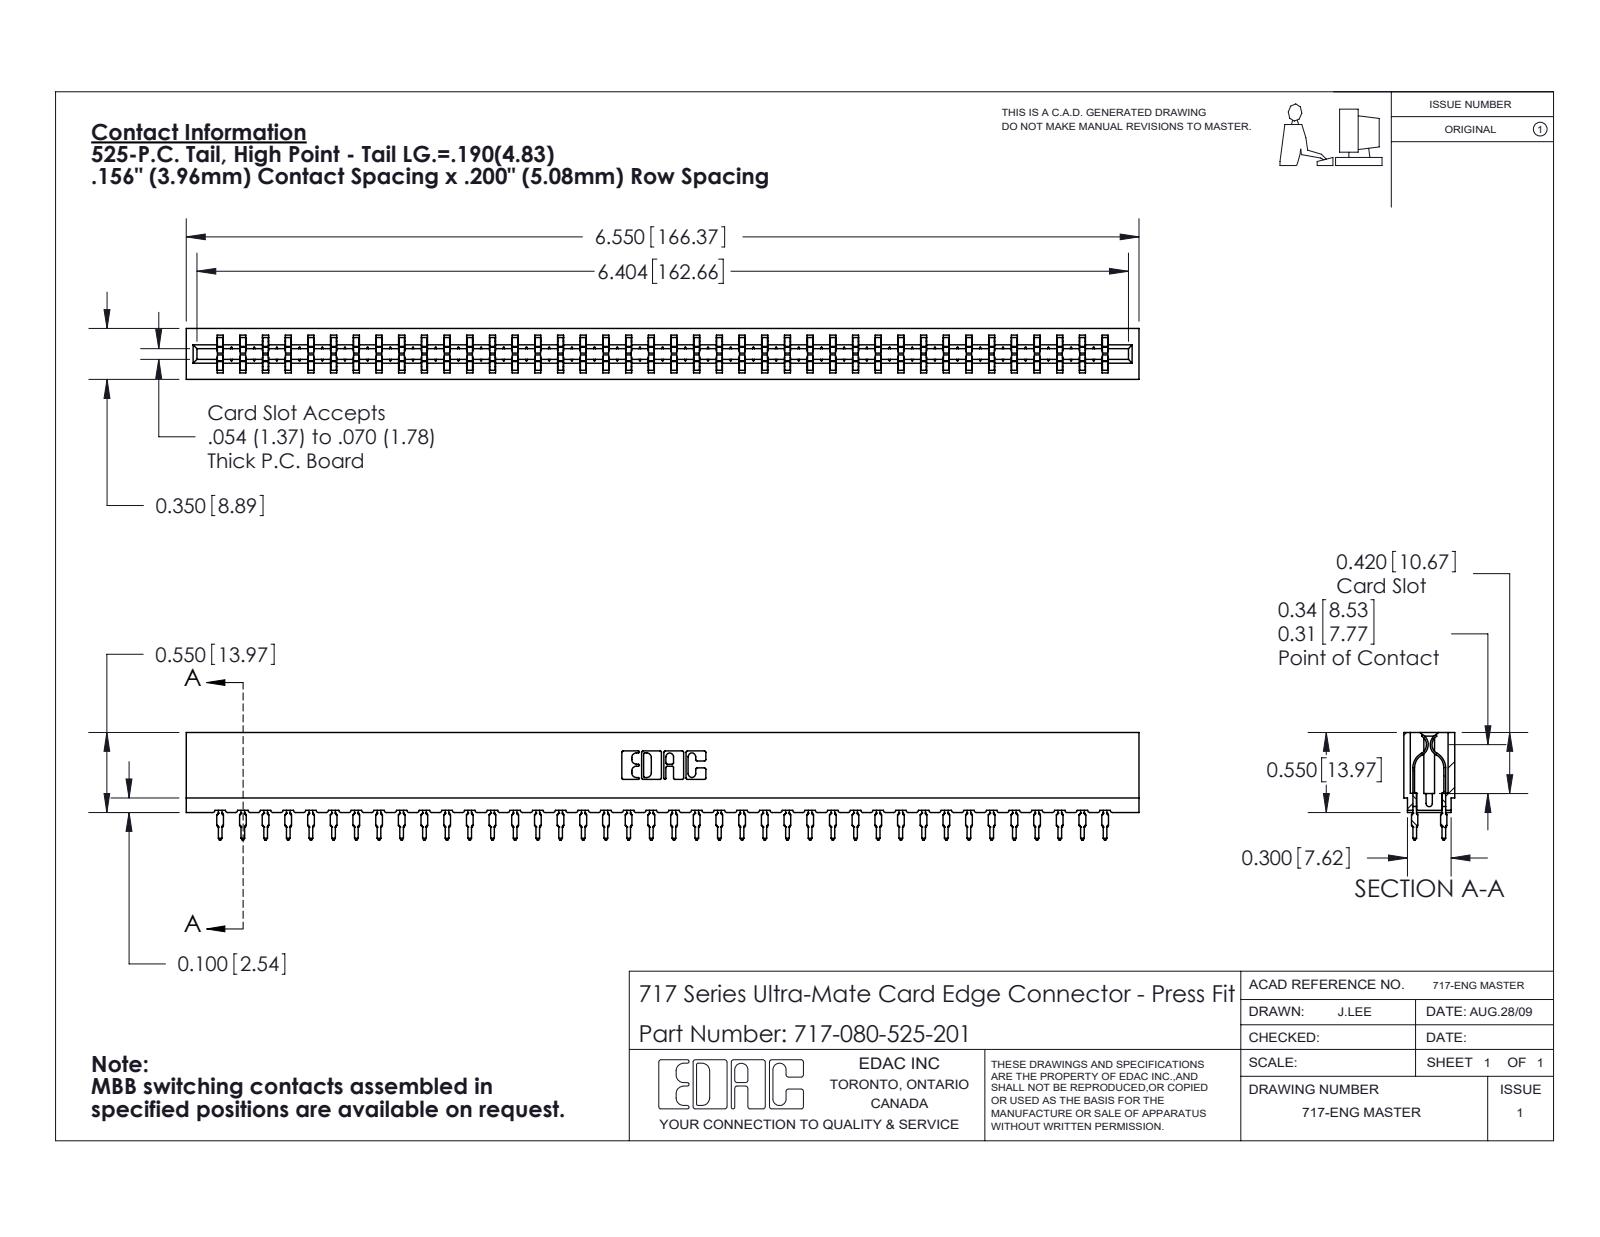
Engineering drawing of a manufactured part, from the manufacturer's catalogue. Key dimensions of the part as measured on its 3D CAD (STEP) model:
Part name (STEP PRODUCT): 717-080-525-201; 717 Part_Insulator Option - 06; 745-292-001_525
STEP written by: SolidWorks 2020 (CONFIG_CONTROL_DESIGN)
Units: inches
Bodies: 81 solids, 7294 faces (3774 planar, 1440 cylindrical, 2080 other)
Overall size (bounding box): 6.55 × 0.739 × 0.35
Volume: 0.879 in³ · Surface area: 33.97 in²
Partial cylindrical surfaces — rounded edges, fillets, slot ends (radius × count): R0.021 ×160, R0.015 ×80, R0.01 ×22, R0.005 ×8, R0.011 ×8, R0.007 ×6, R0.031 ×6, R0.026 ×3
Main face-to-face distances: 0.212, 0.138, 0.35, 0.063, 0.287, 0.076, 0.149, 0.074, 0.045, 0.305
